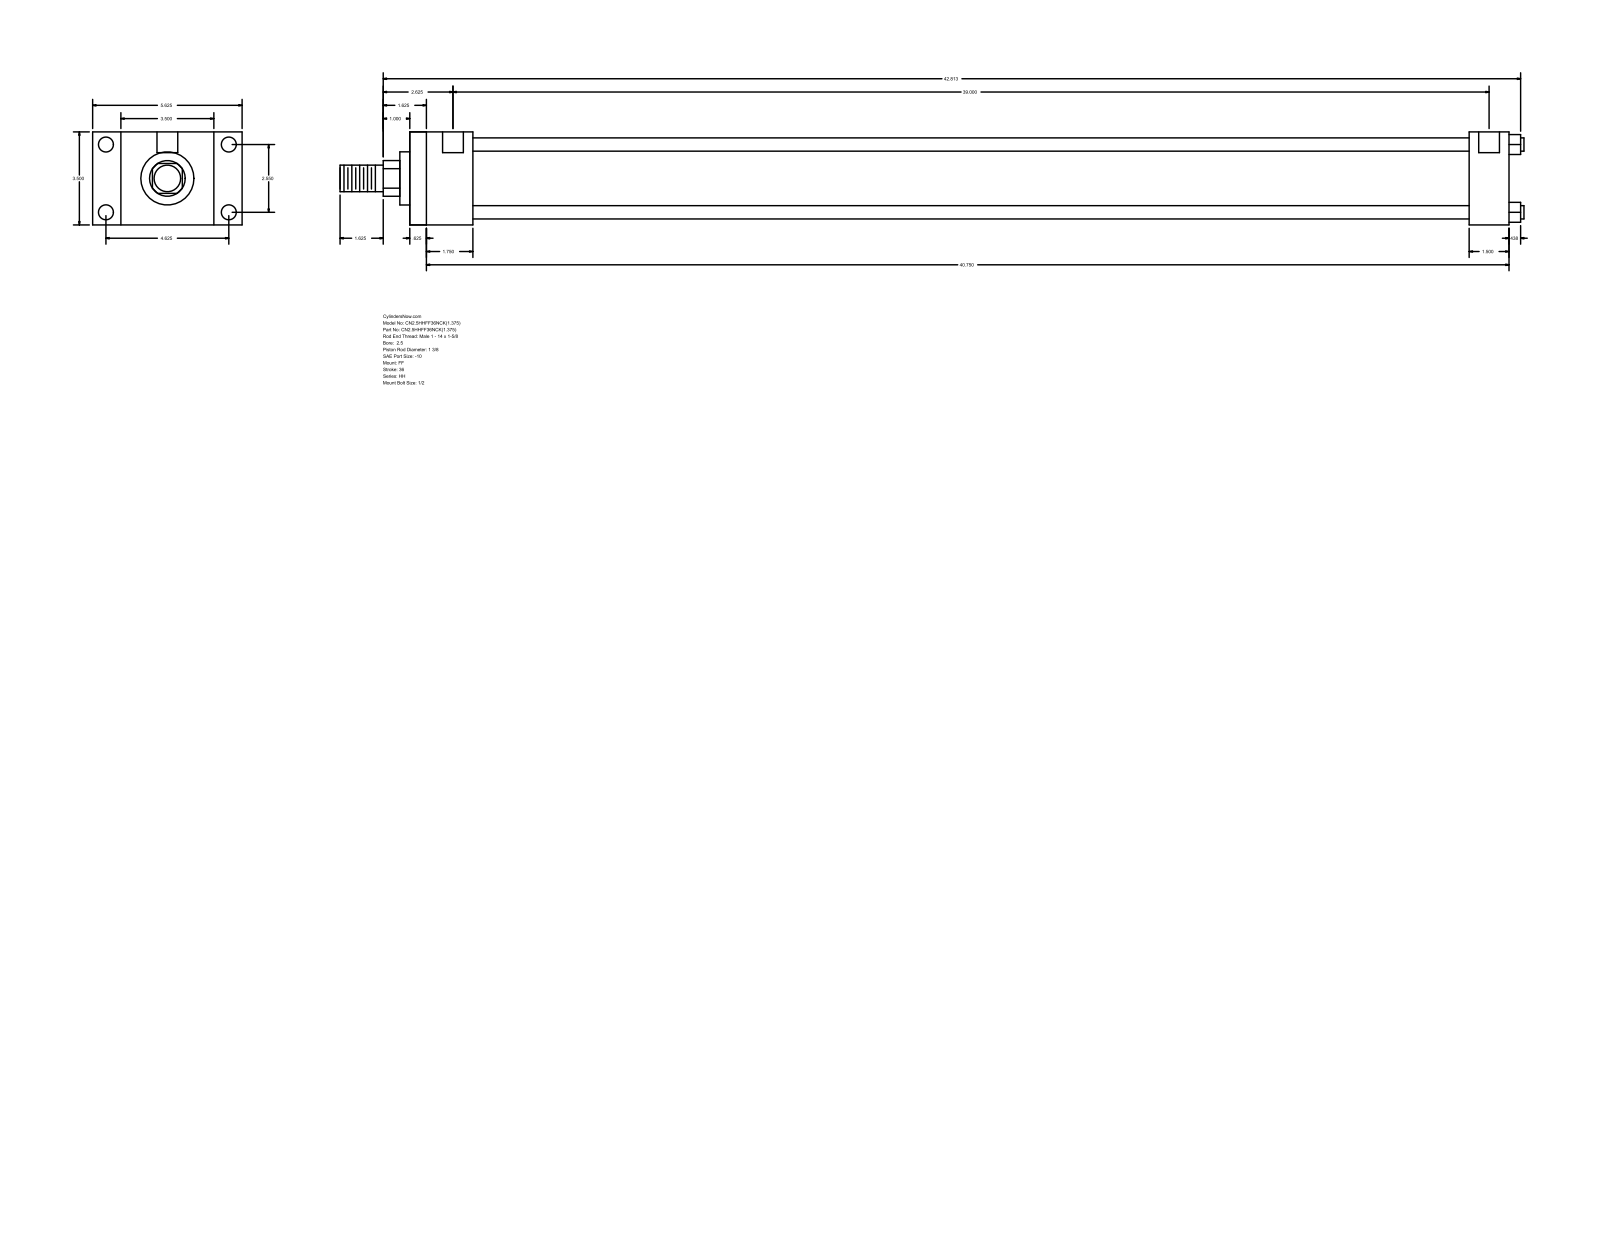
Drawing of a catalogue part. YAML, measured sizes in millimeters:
part_name: "HH_FF__0250_1.375"
step_written_by: "GSSL Pune (CONFIG_CONTROL_DESIGN)"
units: millimeters
bodies: {solids: 0, faces: 92, planar: 64, cylindrical: 28, other: 0}
overall_size: [1131.89, 142.88, 88.9]
round_holes:
  - {diameter: 5.56, count: 4}
  - {diameter: 14.3, count: 4}
  - {diameter: 19.84, count: 2}
round_bosses_or_shafts:
  - {diameter: 12.7, count: 4}
  - {diameter: 73.03, count: 1}
  - {diameter: 50.8, count: 1}
  - {diameter: 34.92, count: 1}
  - {diameter: 25.4, count: 1}
partial_cylinders:
  - {radius: 17.06, count: 1}
face_to_face_distances: [88.9, 1050.93, 15.87, 1035.06, 60.32, 44.45, 990.61, 1012.82, 996.95, 952.5]
hole_center_spacings: [1.58, 64.76, 117.48, 134.15, 992.19, 993.77, 990.61]
